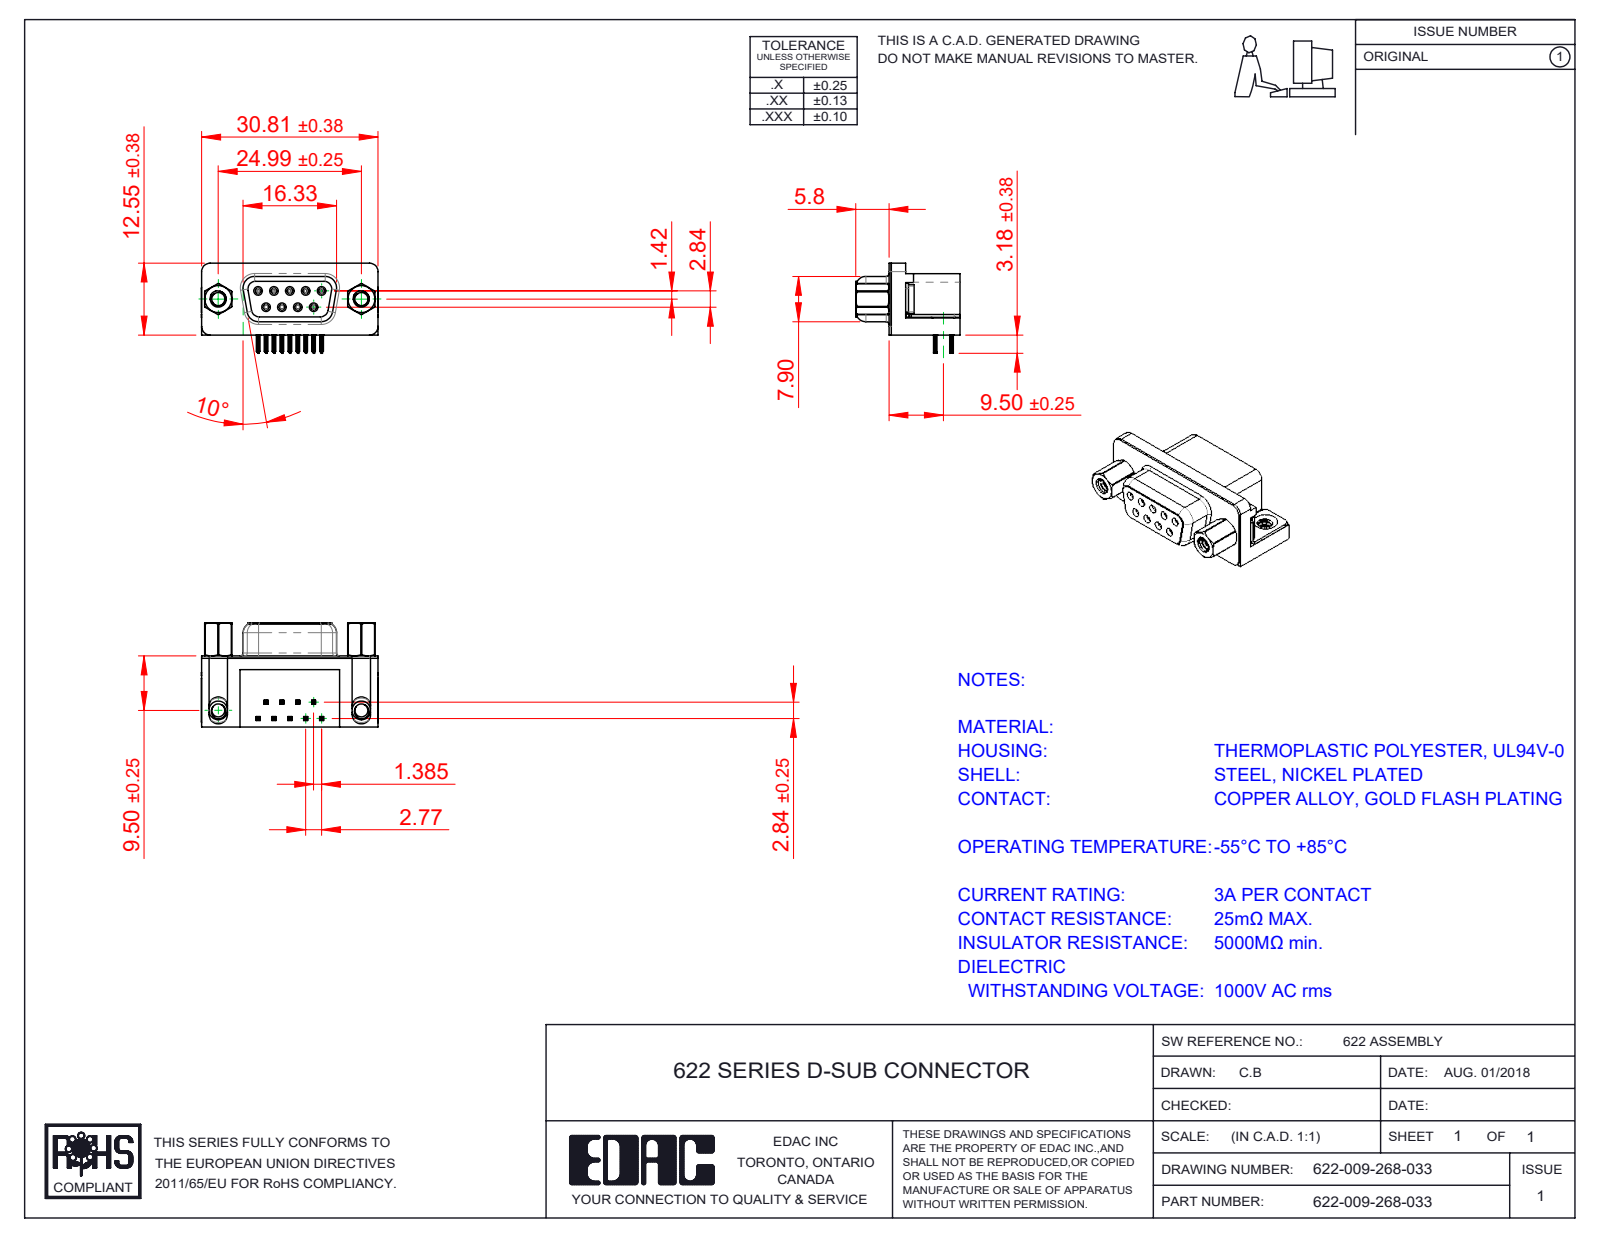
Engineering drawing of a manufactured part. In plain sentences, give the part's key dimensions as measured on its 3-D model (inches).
The part is named "622-009-268-033; 622 4-40 Threaded Rivet; 622 Housing_9 Socket; 622 Contact Top (+4 more)". Its 3-D file was written by "SolidWorks 2016 (CONFIG_CONTROL_DESIGN)". It is 17 solids with 1732 faces: 738 planar, 488 cylindrical and 506 other. Overall it measures 1.216 by 0.717 by 0.64 inches. Its volume is 0.24 cubic inches and its surface area 8.575 square inches. Round holes: 9 of diameter 0.031, 9 of diameter 0.035, 2 of diameter 0.089, 2 of diameter 0.09, 2 of diameter 0.157, 2 of diameter 0.189, 2 of diameter 0.197. Round bosses or shafts: 9 of diameter 0.047, 2 of diameter 0.193, 2 of diameter 0.187, 2 of diameter 0.154, 2 of diameter 0.11. Partial cylindrical surfaces (rounded edges, fillets, slot ends): 72 of radius 0.004, 36 of radius 0.006, 18 of radius 0.014, 18 of radius 0.039, 10 of radius 0.02, 9 of radius 0.013, 8 of radius 0.01, 8 of radius 0.053. The main face-to-face distances are 0.016, 0.472, 0.488, 0.244, 0.014, 0.114, 0.098, 0.407, 0.02, 0.228. The hole center spacings are 0.124, 0.109, 0.218, 0.198, 0.198, 0.327, 0.294, 0.295.
